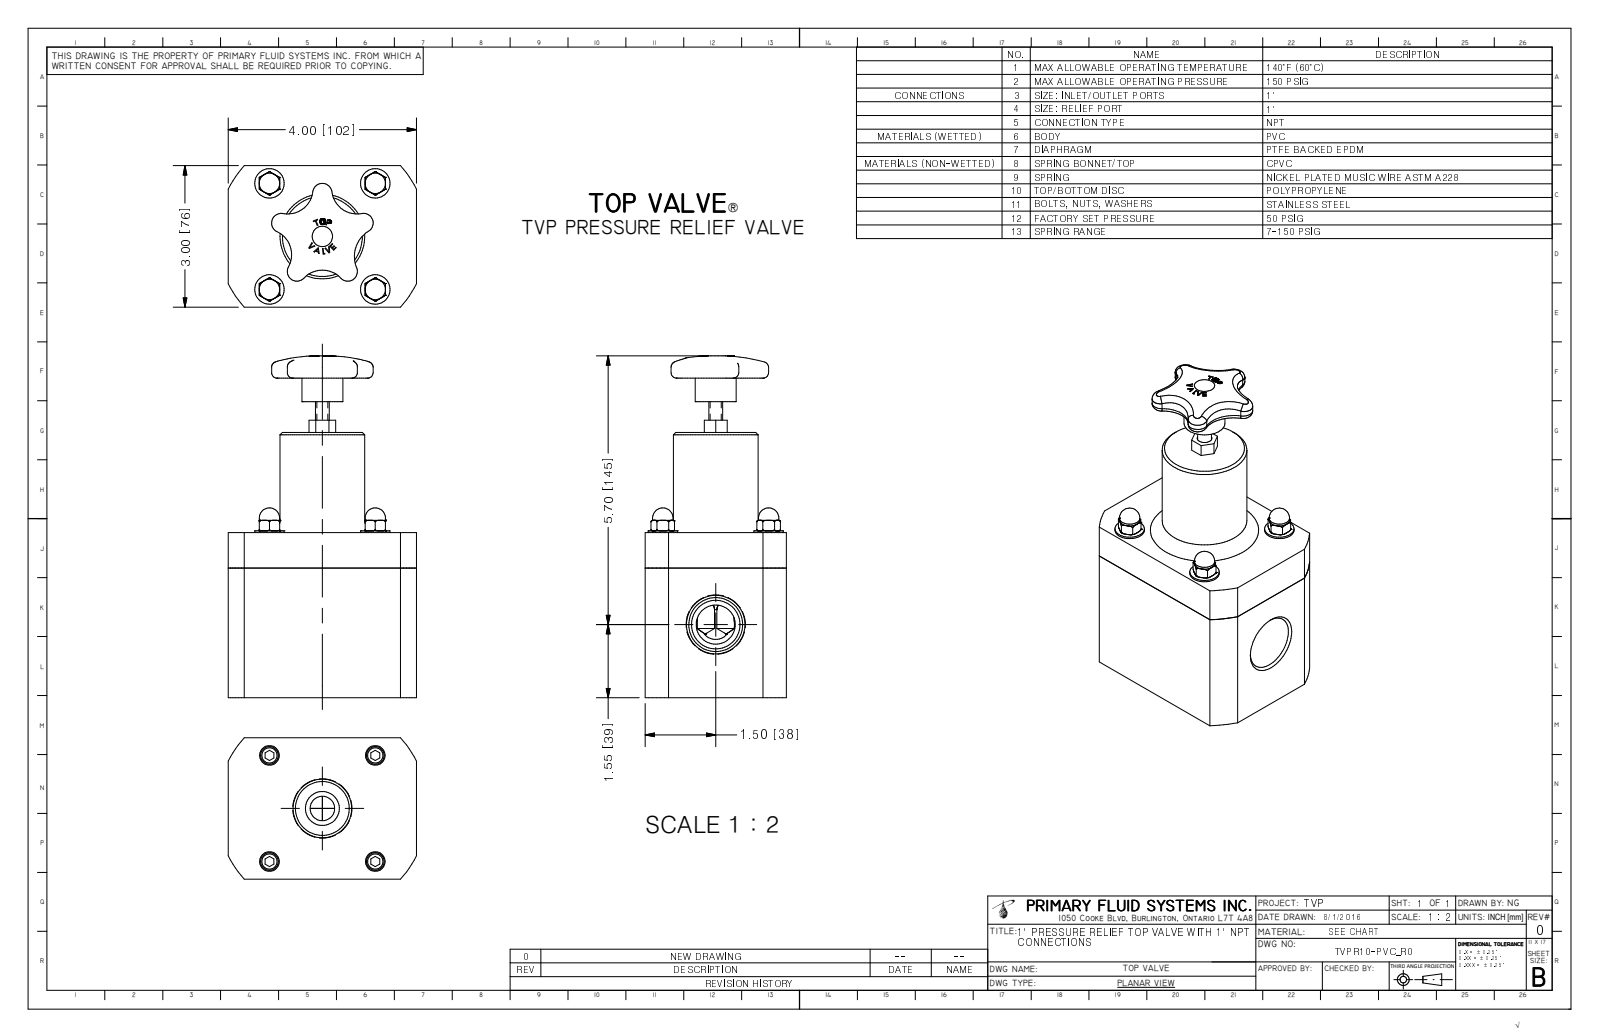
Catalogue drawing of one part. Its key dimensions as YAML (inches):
part_name: "TVPR10-PVC_R0"
step_written_by: "Autodesk Inventor 2009 (AUTOMOTIVE_DESIGN)"
units: inches
bodies: {solids: 1, faces: 344, planar: 147, cylindrical: 48, other: 149}
overall_size: [7.25, 4, 3]
volume: 45.18
surface_area: 107.4
round_holes:
  - {diameter: 0.175, count: 4}
  - {diameter: 1.144, count: 2}
  - {diameter: 2.525, count: 1}
round_bosses_or_shafts:
  - {diameter: 0.625, count: 4}
  - {diameter: 0.433, count: 4}
  - {diameter: 0.375, count: 4}
  - {diameter: 2.5, count: 1}
  - {diameter: 1.8, count: 1}
  - {diameter: 0.87, count: 1}
  - {diameter: 0.293, count: 1}
partial_cylinders:
  - {radius: 0.085, count: 5}
  - {radius: 0.205, count: 5}
  - {radius: 0.536, count: 4}
  - {radius: 0.656, count: 4}
  - {radius: 0.625, count: 1}
  - {radius: 0.745, count: 1}
  - {radius: 2.238, count: 1}
face_to_face_distances: [3, 3.5, 4, 5.625, 2.125, 1, 2, 0.6, 2.9, 5.025]
hole_center_spacings: [2.25, 1.591, 3.182, 1.591, 1.591]
